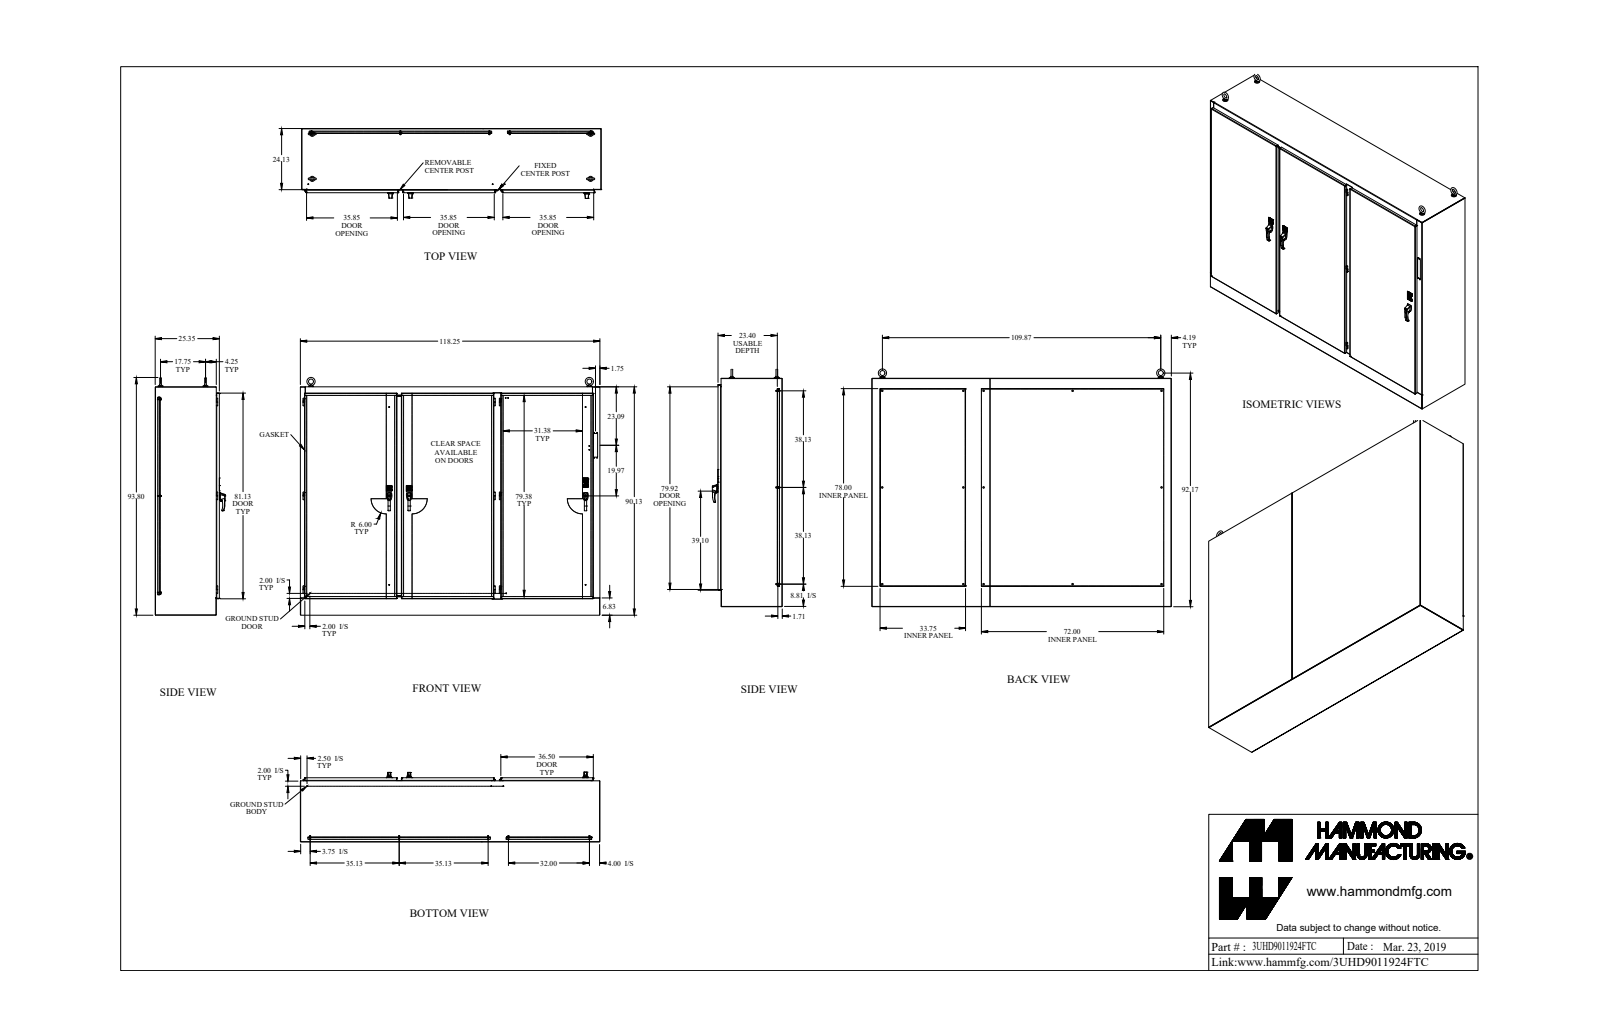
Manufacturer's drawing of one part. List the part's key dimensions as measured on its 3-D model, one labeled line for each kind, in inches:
Part name (STEP PRODUCT): 3UHD9011924FTC
STEP written by: SolidWorks 2018 (AUTOMOTIVE_DESIGN)
Units: inches
Bodies: 309 solids, 4314 faces (2624 planar, 1208 cylindrical, 482 other)
Overall size (bounding box): 118.25 × 93.799 × 27.589
Volume: 5 106 in³ · Surface area: 95 458 in²
Round holes (diameter × count): ⌀0.25 ×22, ⌀0.196 ×19, ⌀0.307 ×17, ⌀0.281 ×12, ⌀0.313 ×9, ⌀0.35 ×9, ⌀0.445 ×9, ⌀0.875 ×8, ⌀0.257 ×6, ⌀0.266 ×6, ⌀0.28 ×6, ⌀0.39 ×6
Round bosses / shafts (diameter × count): ⌀1 ×22, ⌀0.25 ×18, ⌀0.375 ×15, ⌀0.65 ×14, ⌀0.33 ×14, ⌀0.281 ×11, ⌀0.246 ×10, ⌀0.486 ×7
Partial cylindrical surfaces — rounded edges, fillets, slot ends (radius × count): R0.06 ×76, R0.125 ×70, R0.185 ×52, R0.017 ×48, R0.5 ×42, R0.03 ×18, R0.09 ×18, R0.318 ×18
Main face-to-face distances: 0.125, 0.079, 23.431, 25.369, 25.243, 25.29, 25.165, 1.937, 1.812, 23.353
Hole centre spacings: 2.126, 7.87, 17.75, 38.125, 76.25, 109.874, 109.894, 111.298
